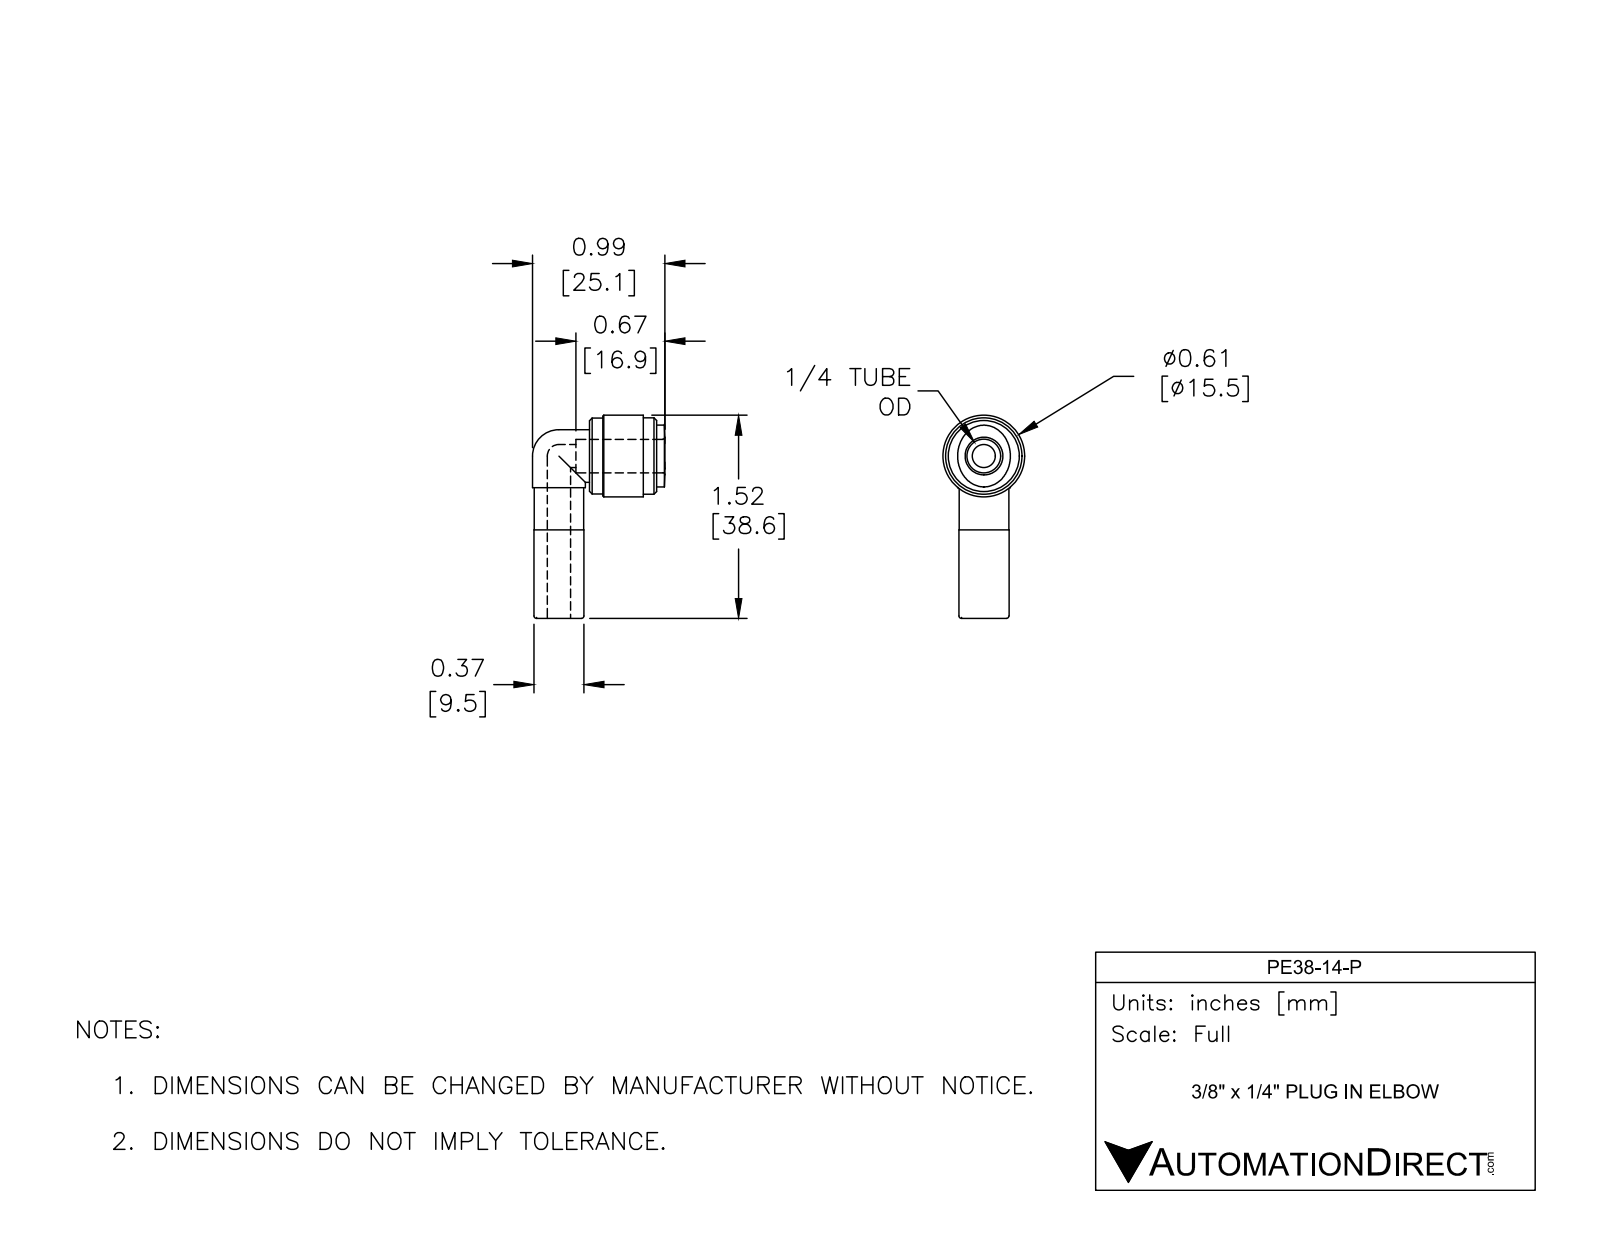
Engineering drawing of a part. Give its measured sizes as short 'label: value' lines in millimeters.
name: PE38-14-P
written by: SolidWorks 2017 (AUTOMOTIVE_DESIGN)
unit: mm
bodies: 1 solid, 46 faces (8 planar, 20 cylindrical, 18 other)
size: 38.6 × 25.1 × 15.5
volume: 3 980 mm³; area: 2 849 mm²
holes: 2× ⌀4.4, 1× ⌀6.4
bosses: 2× ⌀10, 1× ⌀15.5, 1× ⌀14.5, 1× ⌀14.4, 1× ⌀9.5, 1× ⌀9.4
face distances: 12.7, 2.5, 10.2, 2.6, 12.8, 15.3, 5.1, 7.7, 24.8, 16.8
